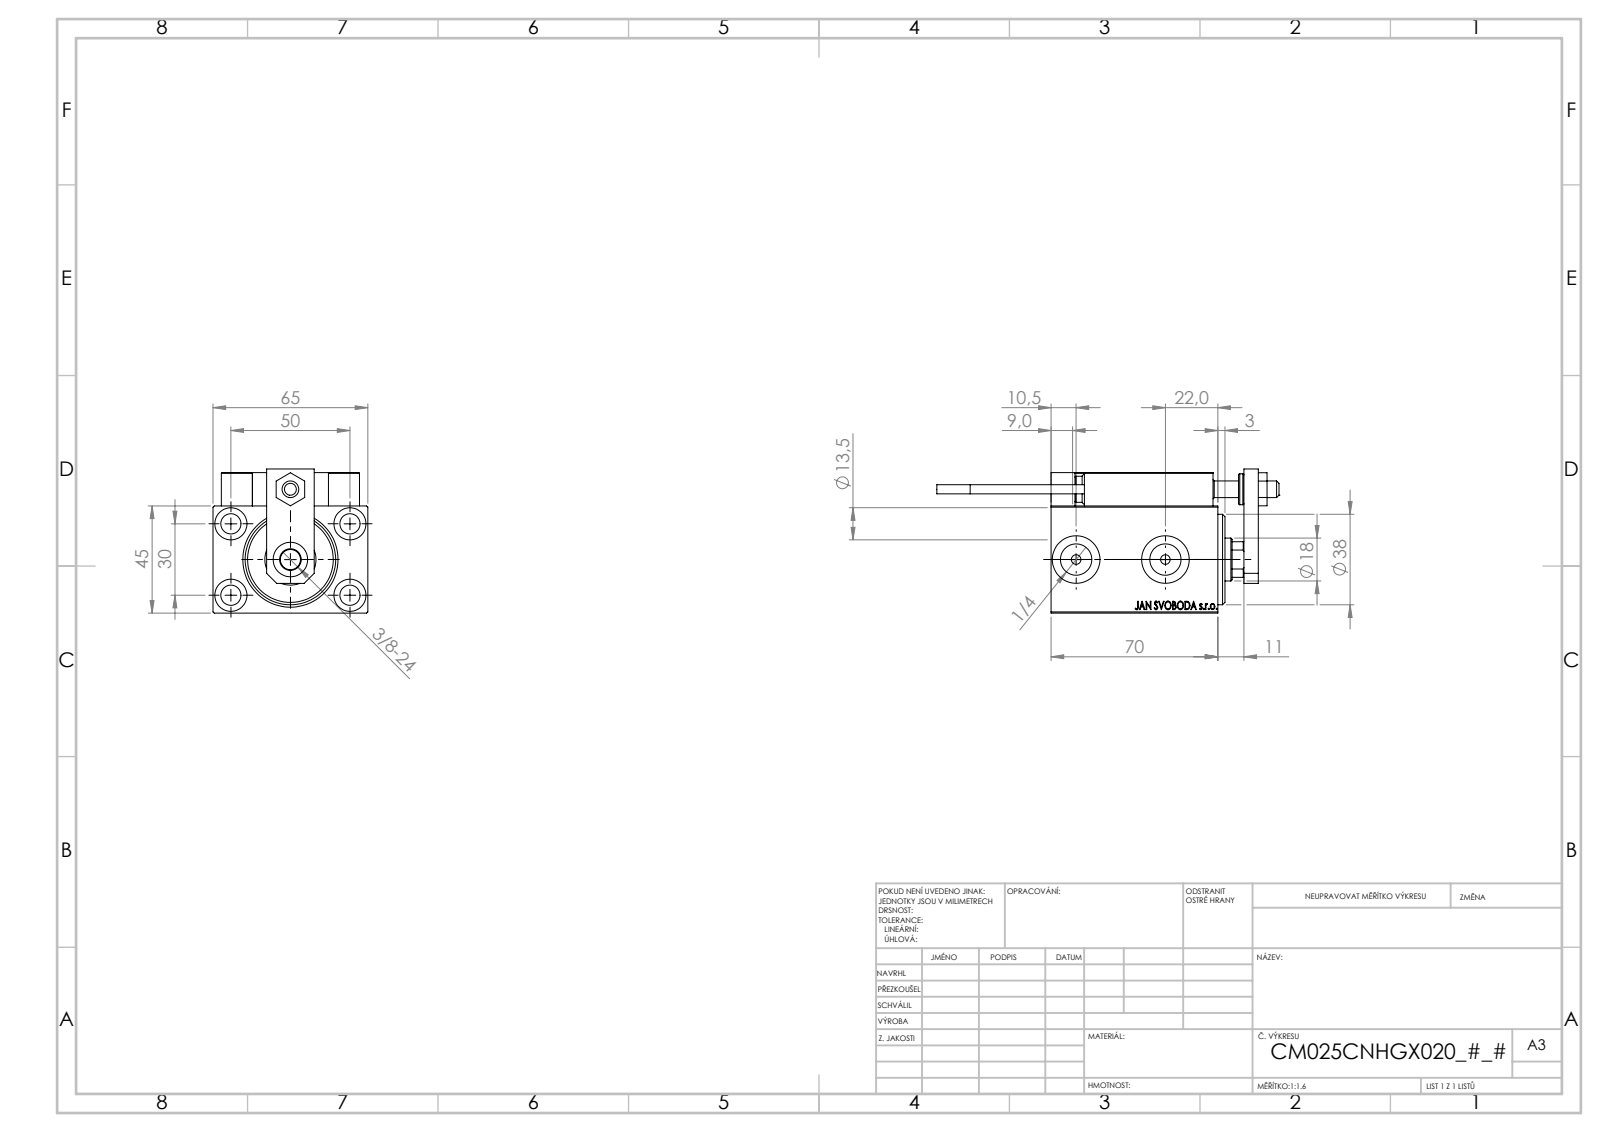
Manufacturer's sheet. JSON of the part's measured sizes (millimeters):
{"part_name": "SWITCH_X_FRONT_BACK; V450CM_C_Body; V450CM_C_VCP; ALLEN BOLT D5 (+7 more)", "step_written_by": "SolidWorks 2019 (CONFIG_CONTROL_DESIGN)", "units": "millimeters", "bodies": {"solids": 23, "faces": 1282, "planar": 560, "cylindrical": 188, "other": 534}, "overall_size": [143.7, 65, 60.5], "volume_mm3": 223122, "surface_area_mm2": 70761, "round_holes": [[4, 6], [8, 5], [8.5, 5], [3.2, 4], [13.5, 4], [5, 2], [13.16, 2], [20, 2], [7, 1], [14.5, 1], [18, 1], [21.5, 1]], "round_bosses_or_shafts": [[5, 2], [3.8, 2], [13, 1], [11, 1]], "partial_cylinders_radius": [[0.3, 30], [3, 2], [8.5, 1]], "face_to_face_distances": [45, 59, 65, 14, 6, 3, 7, 13, 3.5, 5], "hole_center_spacings": [29.15, 11.37, 20, 22.09, 28.9, 29.59, 29.69, 30]}
